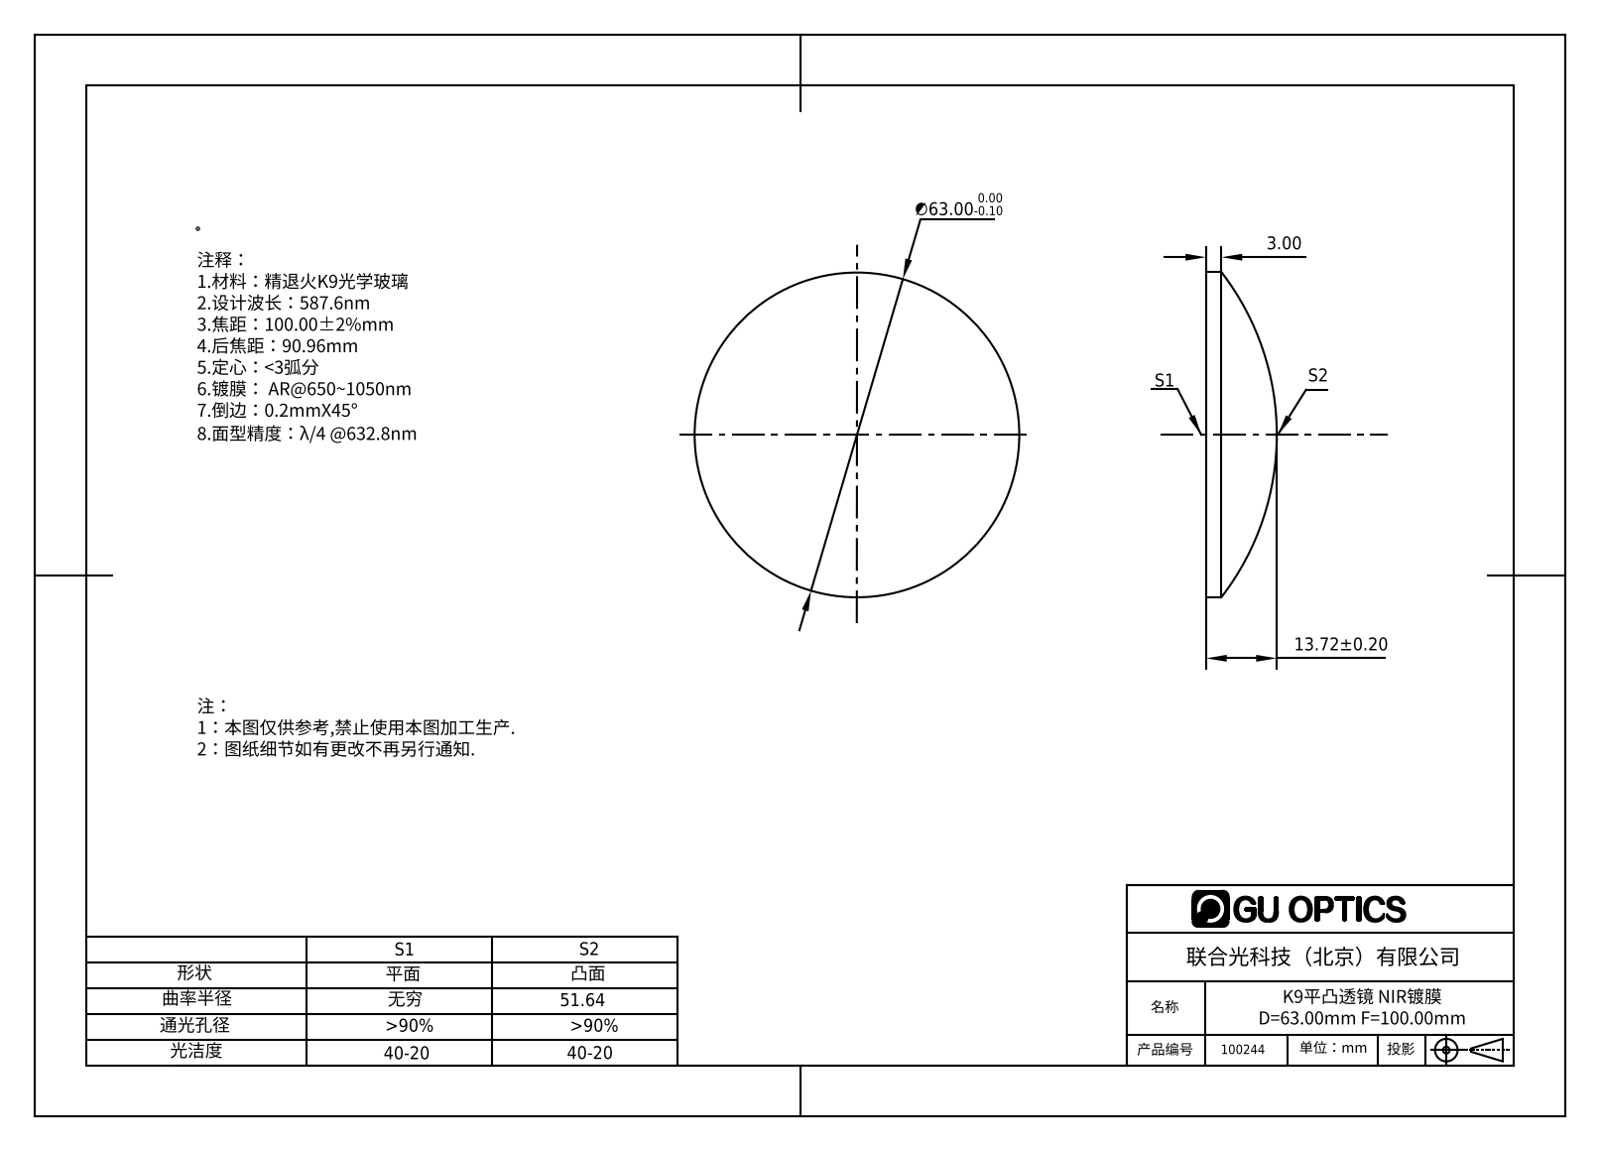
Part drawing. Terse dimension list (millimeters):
name: 100244
written by: SolidWorks 2016 (AUTOMOTIVE_DESIGN)
unit: mm
bodies: 1 solid, 5 faces (1 planar, 2 cylindrical, 2 other)
size: 63 × 63 × 13.72
volume: 26 705 mm³; area: 7 189 mm²
bosses: 1× ⌀63
